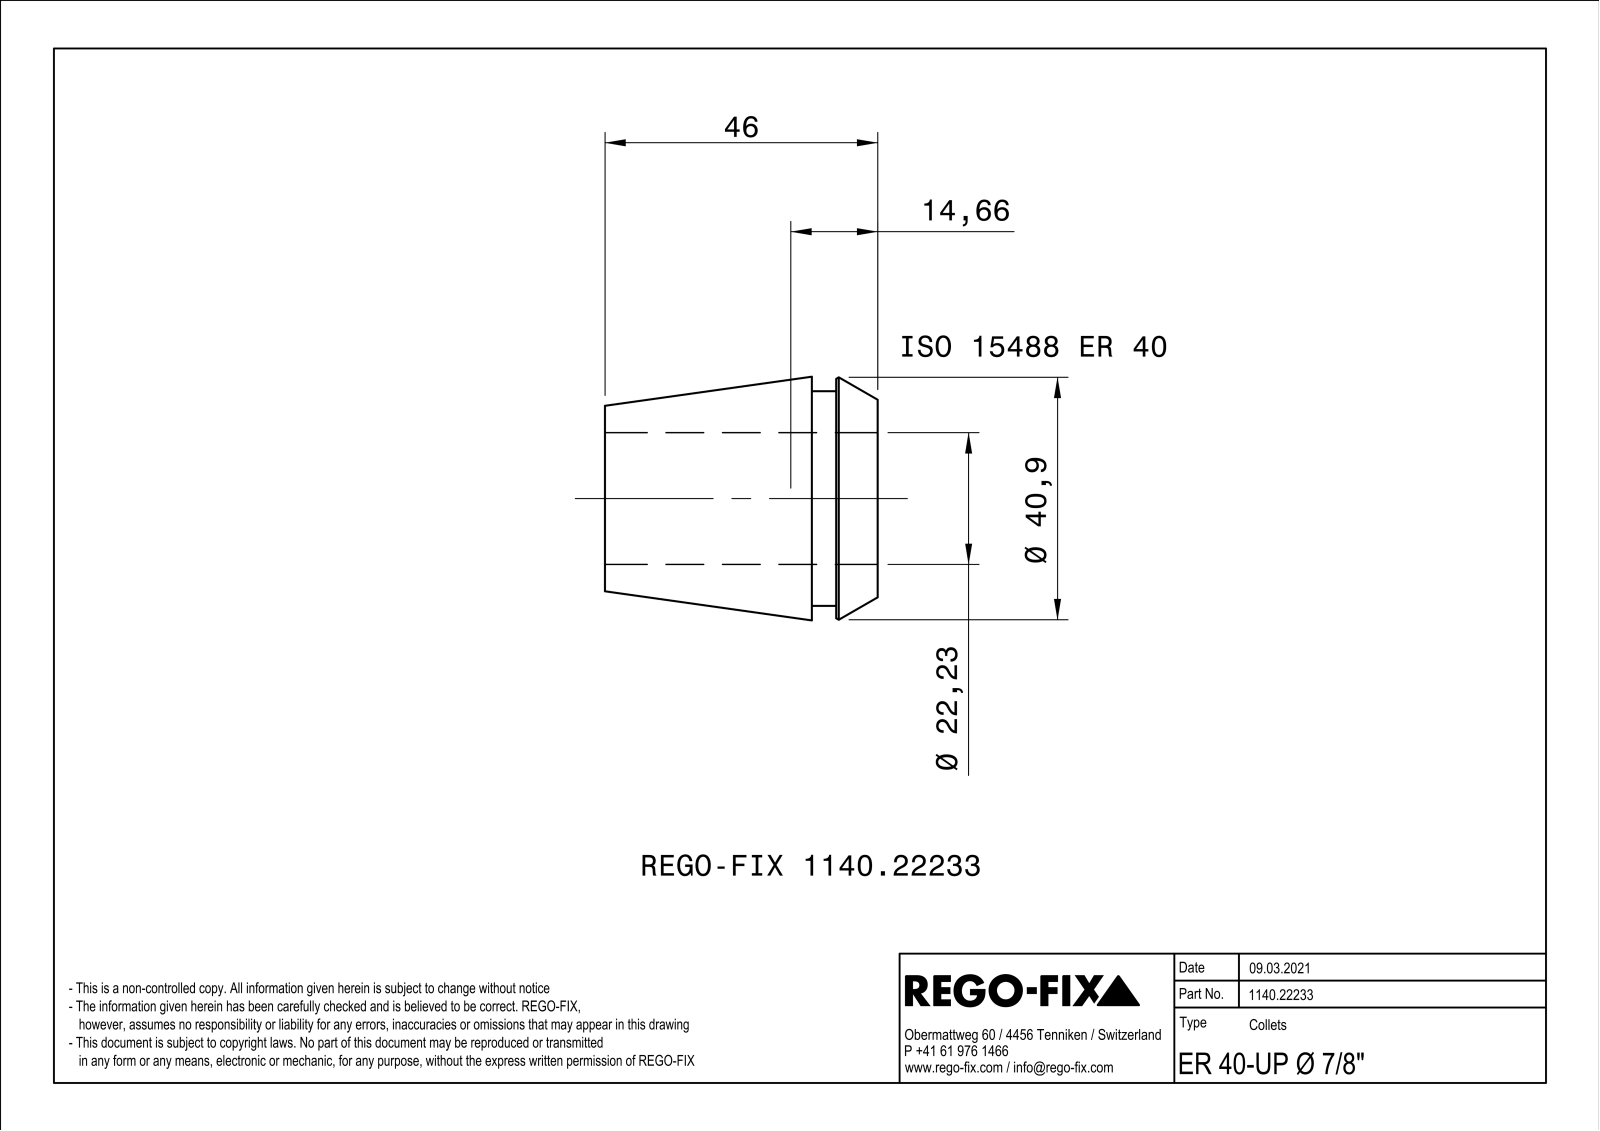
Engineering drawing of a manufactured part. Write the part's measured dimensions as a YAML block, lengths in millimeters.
part_name: "NOCUT"
step_written_by: "SIEMENS PLM Software Solid Edge ST10 (AUTOMOTIVE_DESIGN)"
units: millimeters
bodies: {solids: 1, faces: 177, planar: 88, cylindrical: 9, other: 80}
overall_size: [46, 40.99, 40.99]
volume: 25394
surface_area: 17811
round_holes:
  - {diameter: 22.23, count: 1}
round_bosses_or_shafts:
  - {diameter: 36.2, count: 1}
face_to_face_distances: [1, 46, 11.1, 34.9, 7, 4.1, 39, 7.5, 0.5, 3.6]
